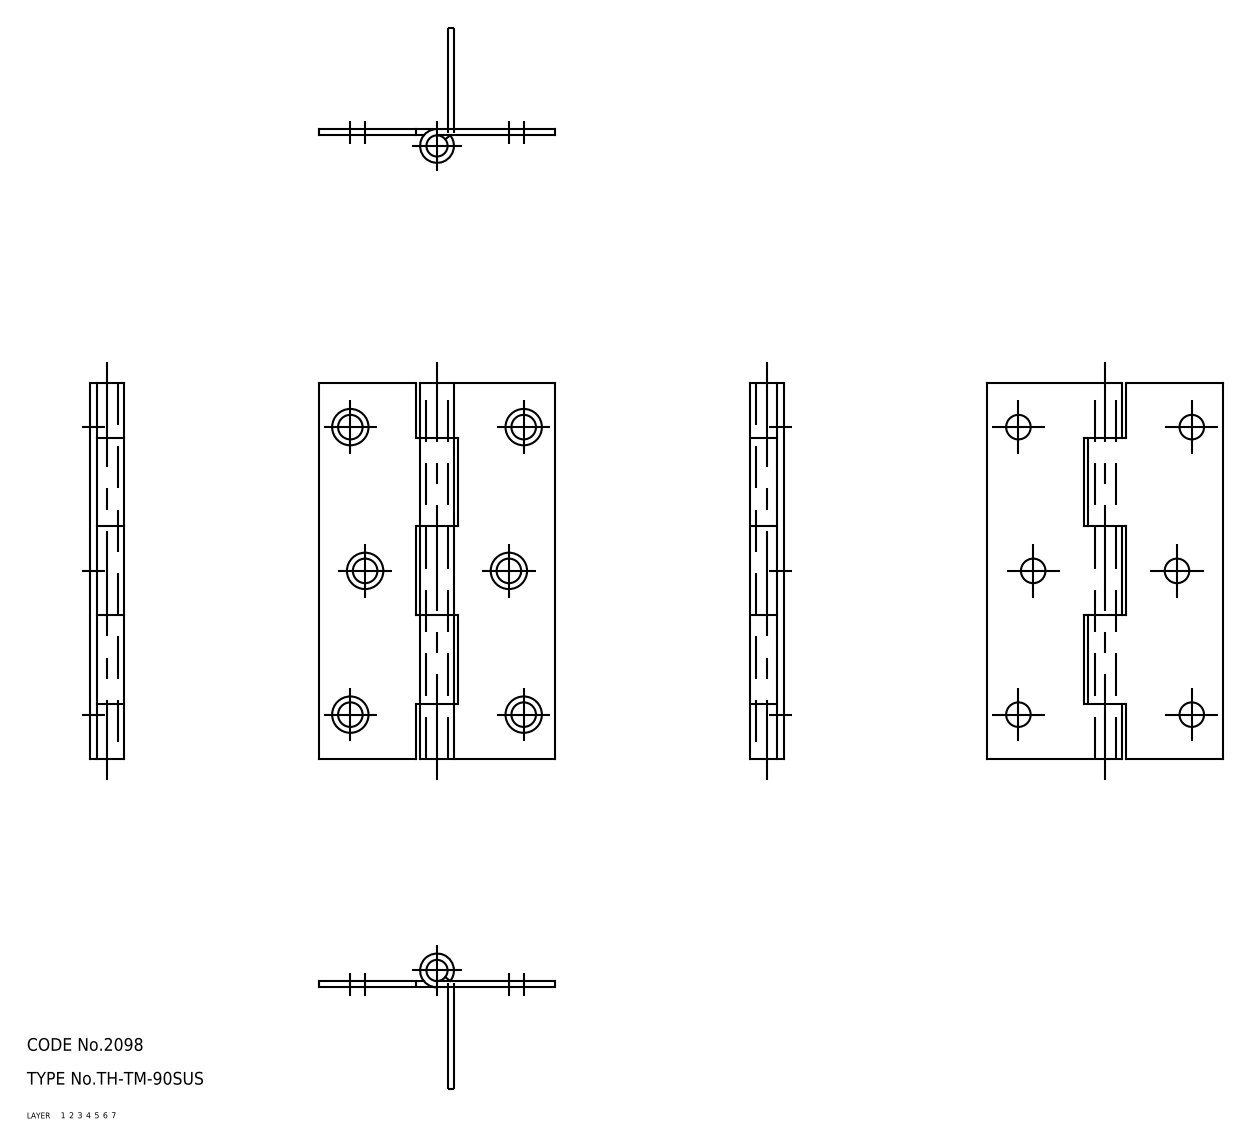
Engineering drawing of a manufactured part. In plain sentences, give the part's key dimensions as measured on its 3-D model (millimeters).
The part is named "shaft; hinge piece_B; hinge piece_A; TH_TM_90SUS_26817_36". Its 3-D file was written by "CADfix (AUTOMOTIVE_DESIGN)". It is 3 solids with 66 faces: 0 planar, 0 cylindrical and 66 other. Overall it measures 89 by 56 by 8 millimeters. Its volume is 10 527 cubic millimeters and its surface area 14 406 square millimeters.
